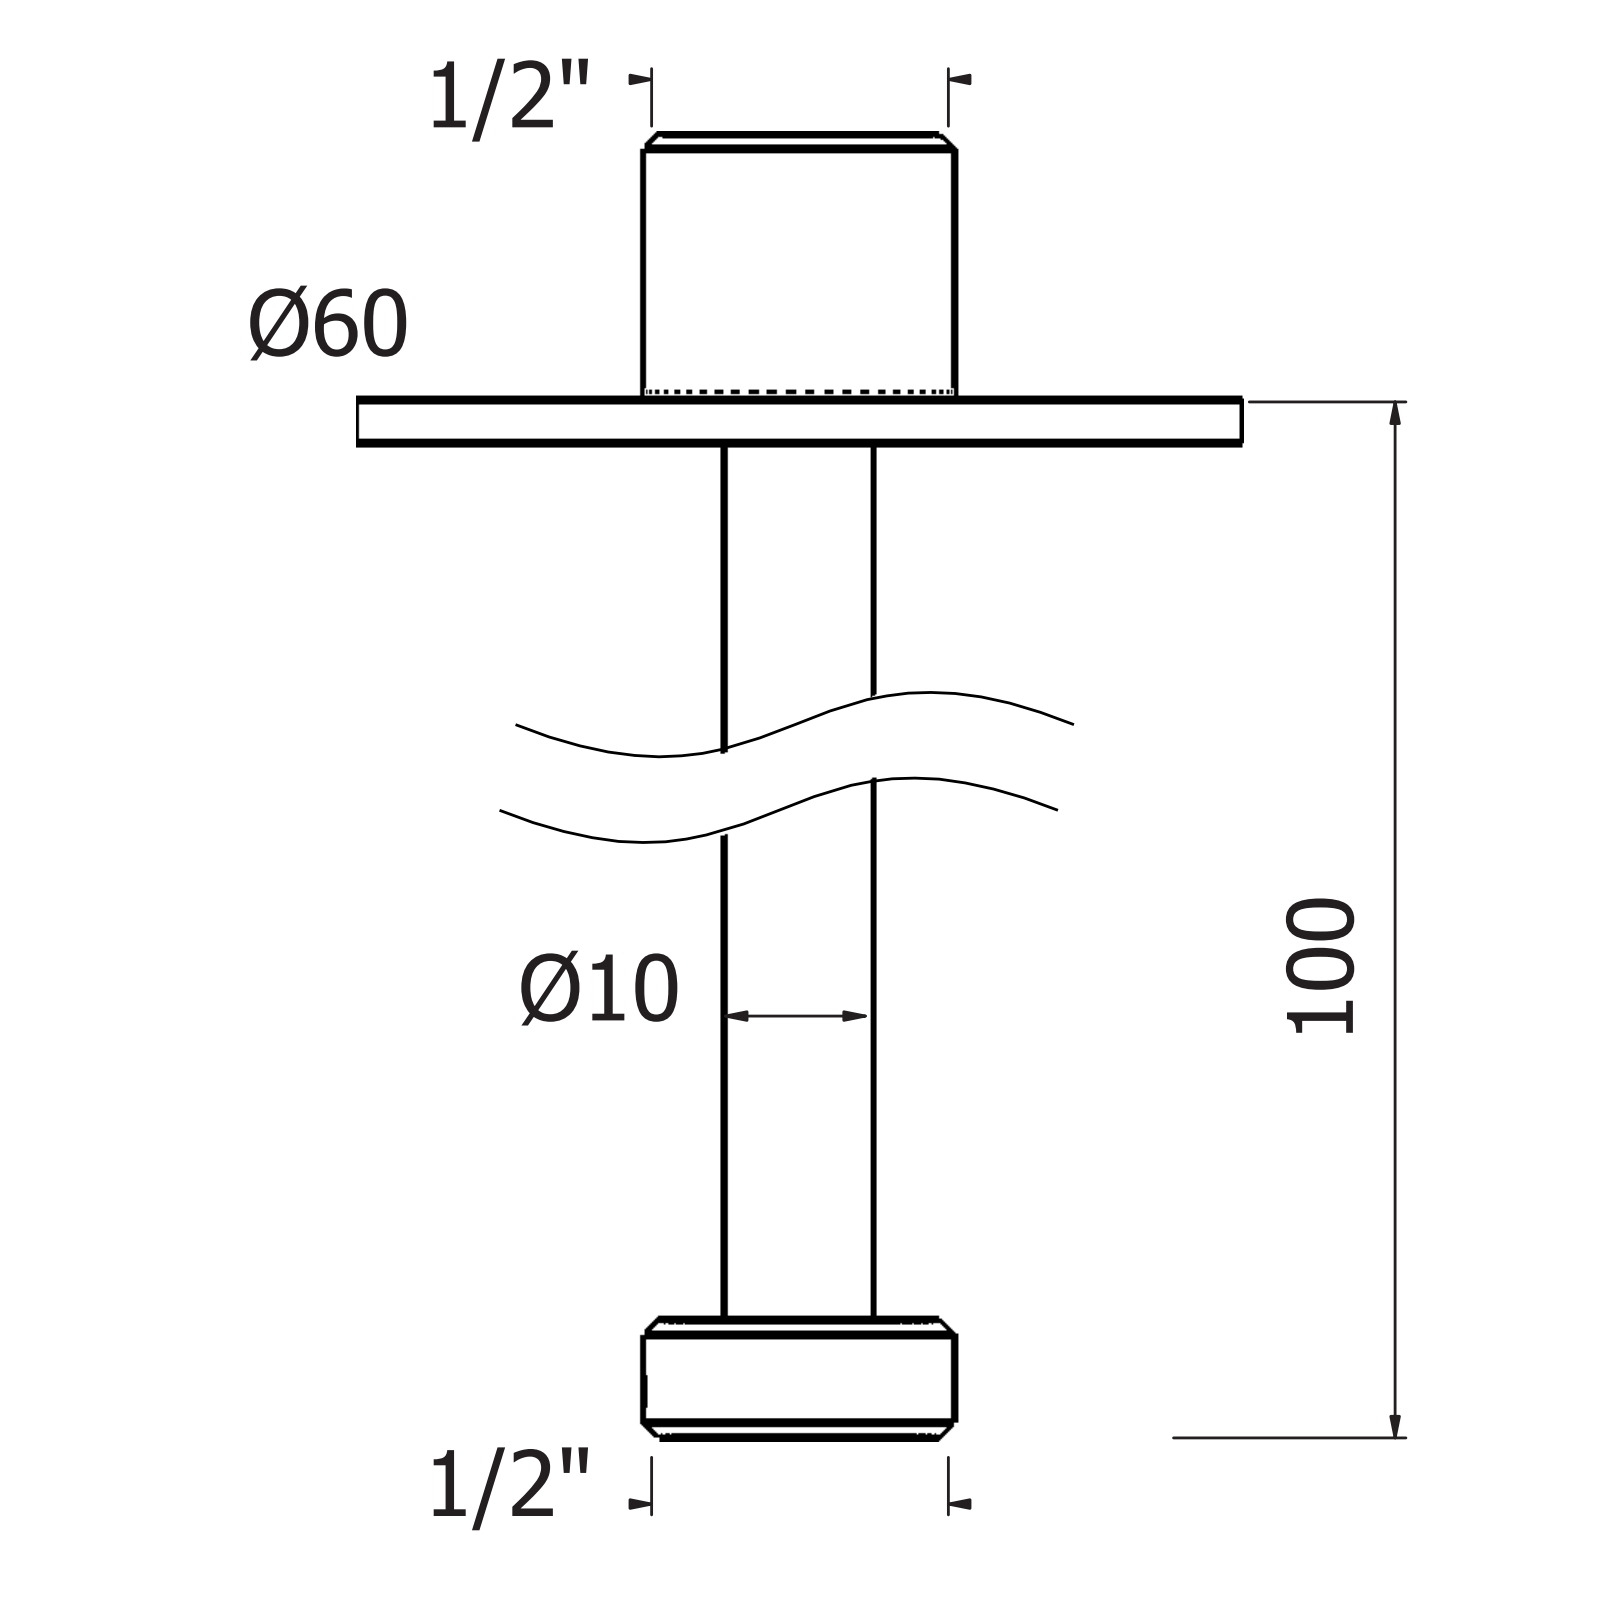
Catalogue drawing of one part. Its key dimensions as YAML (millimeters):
part_name: "A.R._24543/20220905"
step_written_by: "Spatial InterOp 3D (AUTOMOTIVE_DESIGN)"
units: millimeters
bodies: {solids: 1, faces: 24, planar: 10, cylindrical: 9, other: 5}
overall_size: [116.2, 60, 60]
volume: 18710
surface_area: 13907
round_holes:
  - {diameter: 7, count: 1}
  - {diameter: 10.4, count: 1}
  - {diameter: 14, count: 1}
  - {diameter: 16.4, count: 1}
round_bosses_or_shafts:
  - {diameter: 60, count: 1}
  - {diameter: 20.95, count: 1}
  - {diameter: 10, count: 1}
face_to_face_distances: [3, 95.2, 98.2, 8, 87.2, 90.2, 111, 103, 15.8, 12.8]
